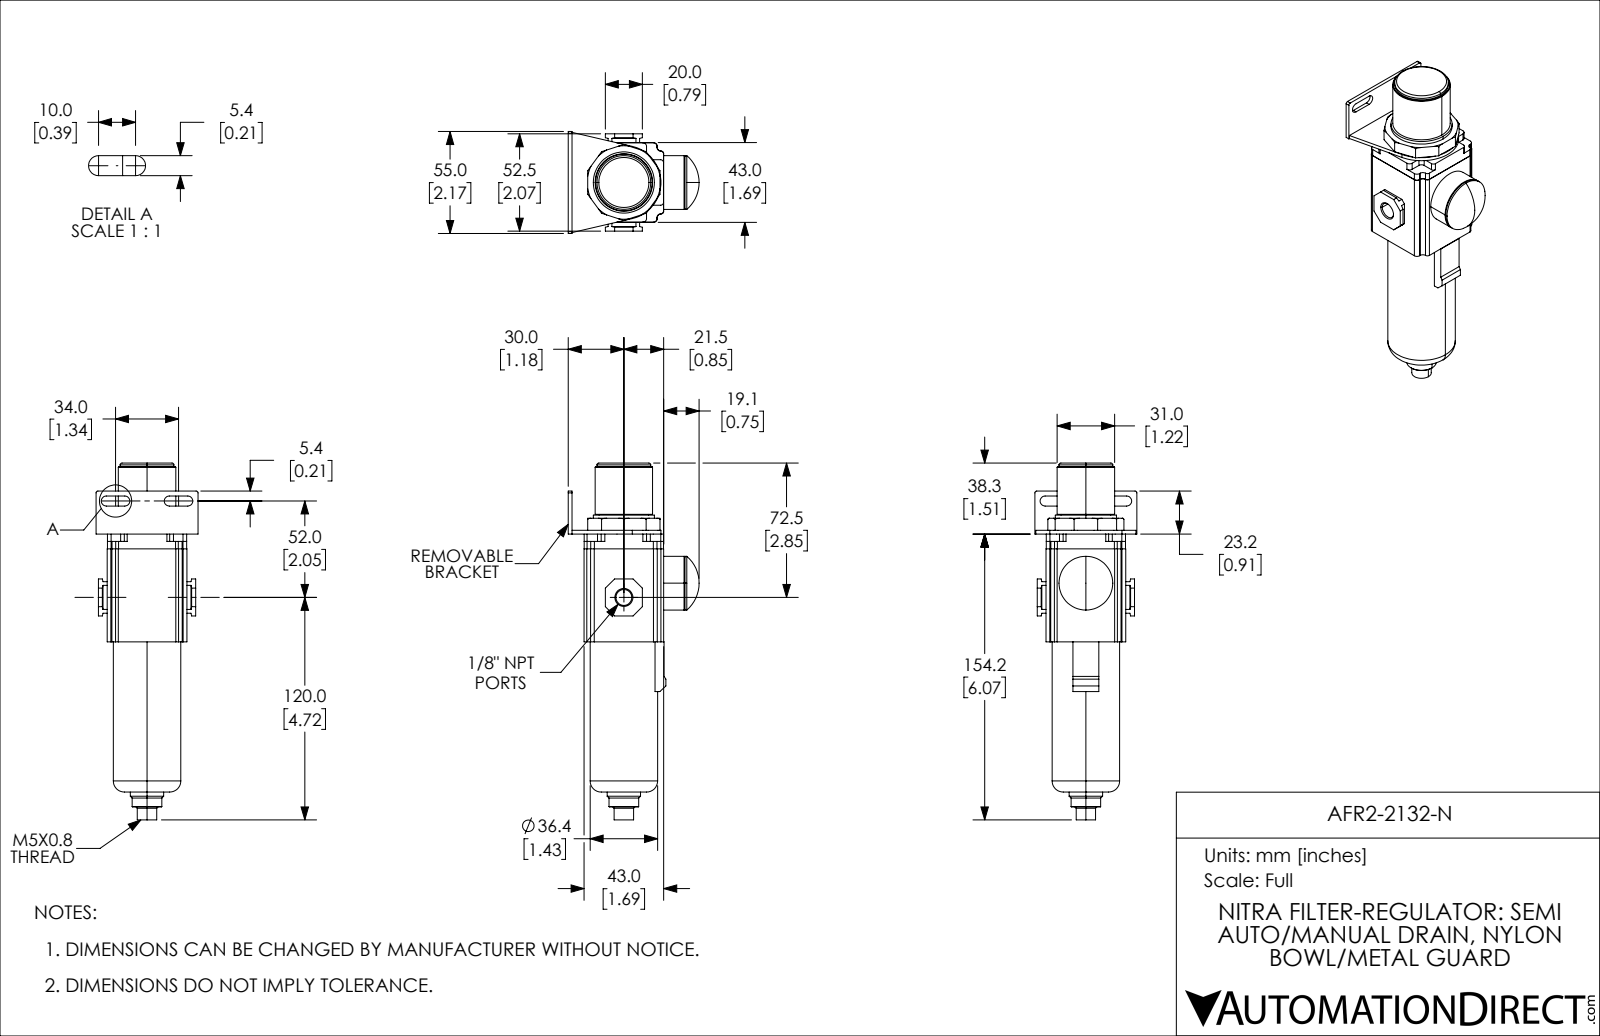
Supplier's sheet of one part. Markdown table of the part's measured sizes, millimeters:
| quantity | value |
| --- | --- |
| part name | AFR2-2132-N |
| STEP written by | SolidWorks 2019 (CONFIG_CONTROL_DESIGN) |
| units | millimeters |
| bodies | 1 solid, 220 faces (119 planar, 69 cylindrical, 32 other) |
| overall size | 192.5 × 70.62 × 55 |
| volume | 238 894 mm³ |
| surface area | 33 696 mm² |
| round holes (diameter × count) | 4.13 × 1, 8.57 × 1 |
| round bosses / shafts (diameter × count) | 29 × 2, 36.4 × 1, 33 × 1, 31 × 1, 26.78 × 1, 18 × 1, 16 × 1, 10.5 × 1 |
| partial cylindrical surfaces (radius × count) | 2 × 24, 1.5 × 12, 2.7 × 4, 1 × 2, 20 × 1 |
| main face-to-face distances | 43, 2, 8.5, 6.5, 49.5, 51.5, 42.9, 36.3, 58.2, 60.2 |
